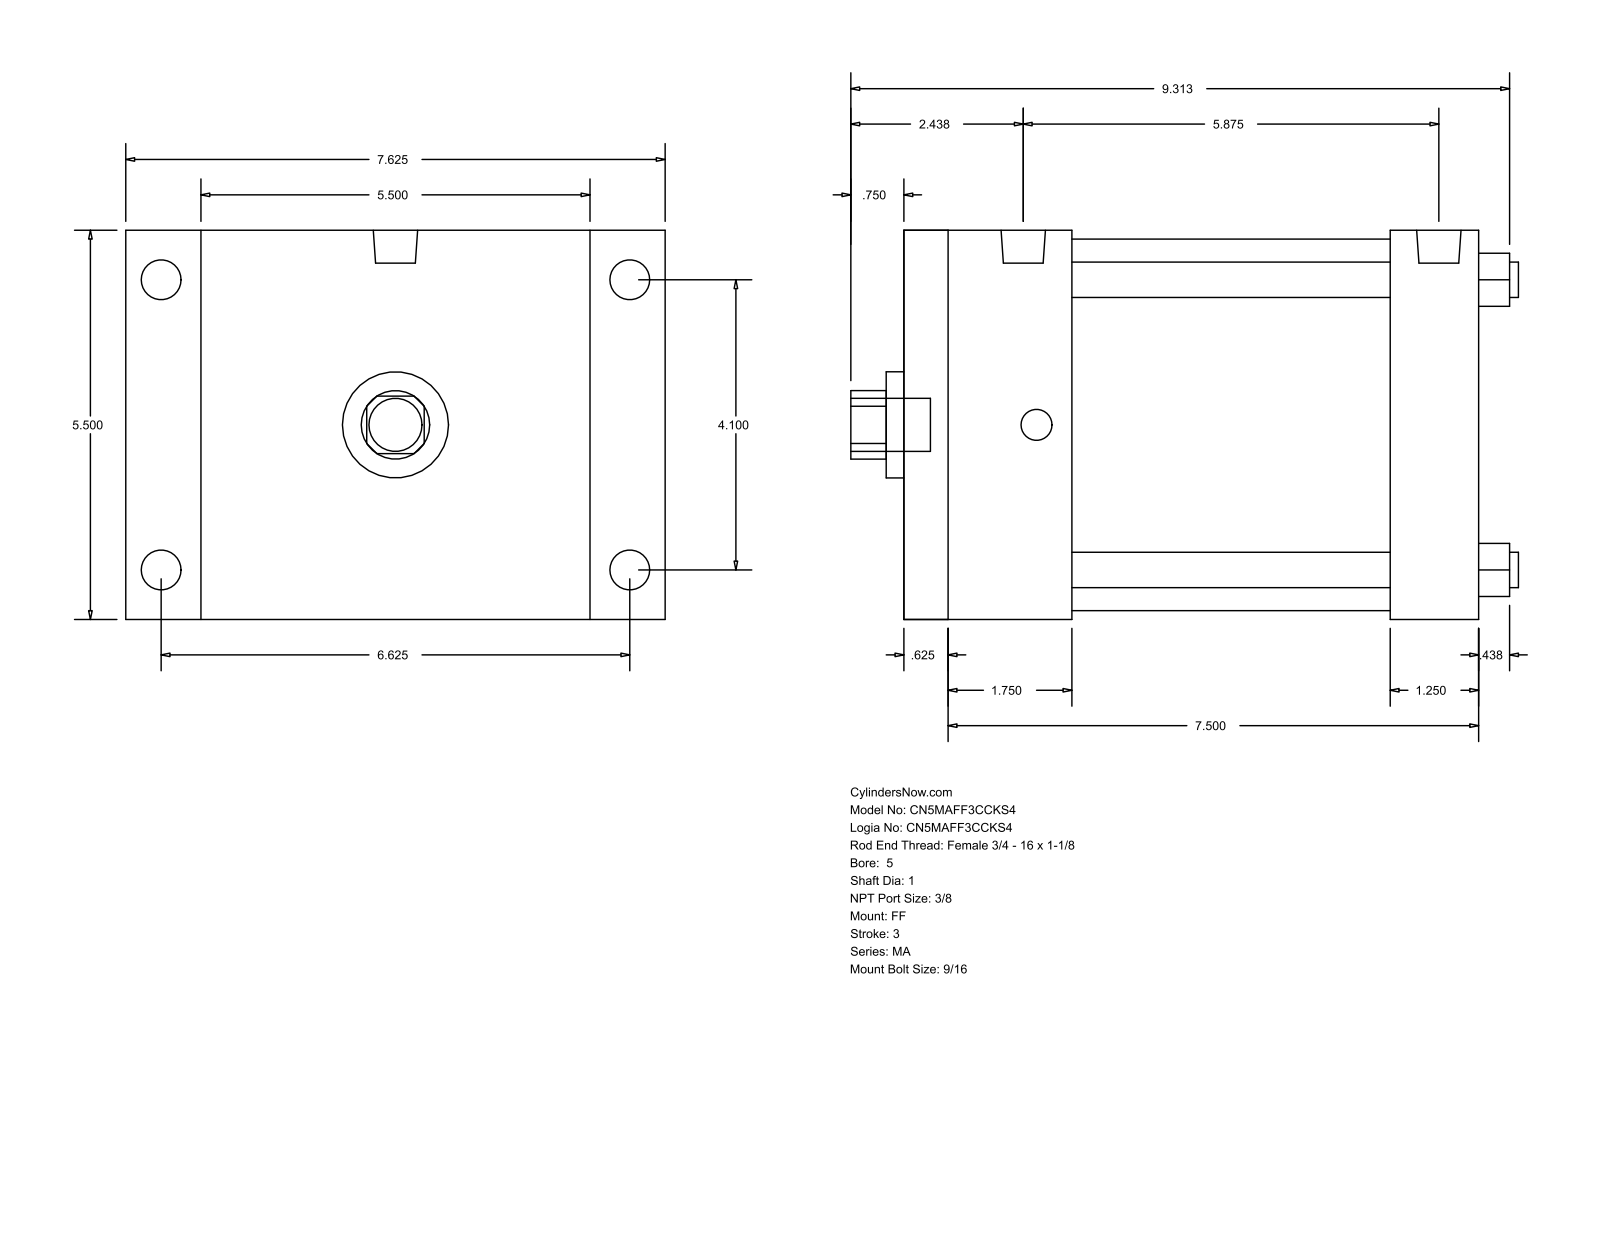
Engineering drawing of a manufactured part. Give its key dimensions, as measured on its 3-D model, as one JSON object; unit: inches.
{"part_name": "MA_FF__0500_1", "step_written_by": "GSSL Pune (CONFIG_CONTROL_DESIGN)", "units": "inches", "bodies": {"solids": 0, "faces": 92, "planar": 64, "cylindrical": 28, "other": 0}, "overall_size": [9.437, 7.625, 5.5], "round_holes": [[0.5, 4], [1, 1], [1.5, 1], [5.25, 1]], "round_bosses_or_shafts": [[0.563, 4], [0.437, 4], [0.627, 2], [0.75, 1]], "partial_cylinders_radius": [[0.484, 1]], "face_to_face_distances": [5.5, 8.125, 0.625, 7.5, 6.875, 6.25, 1.25, 2.375, 1.75, 4.5], "hole_center_spacings": [2.899, 4.1, 5.798]}
